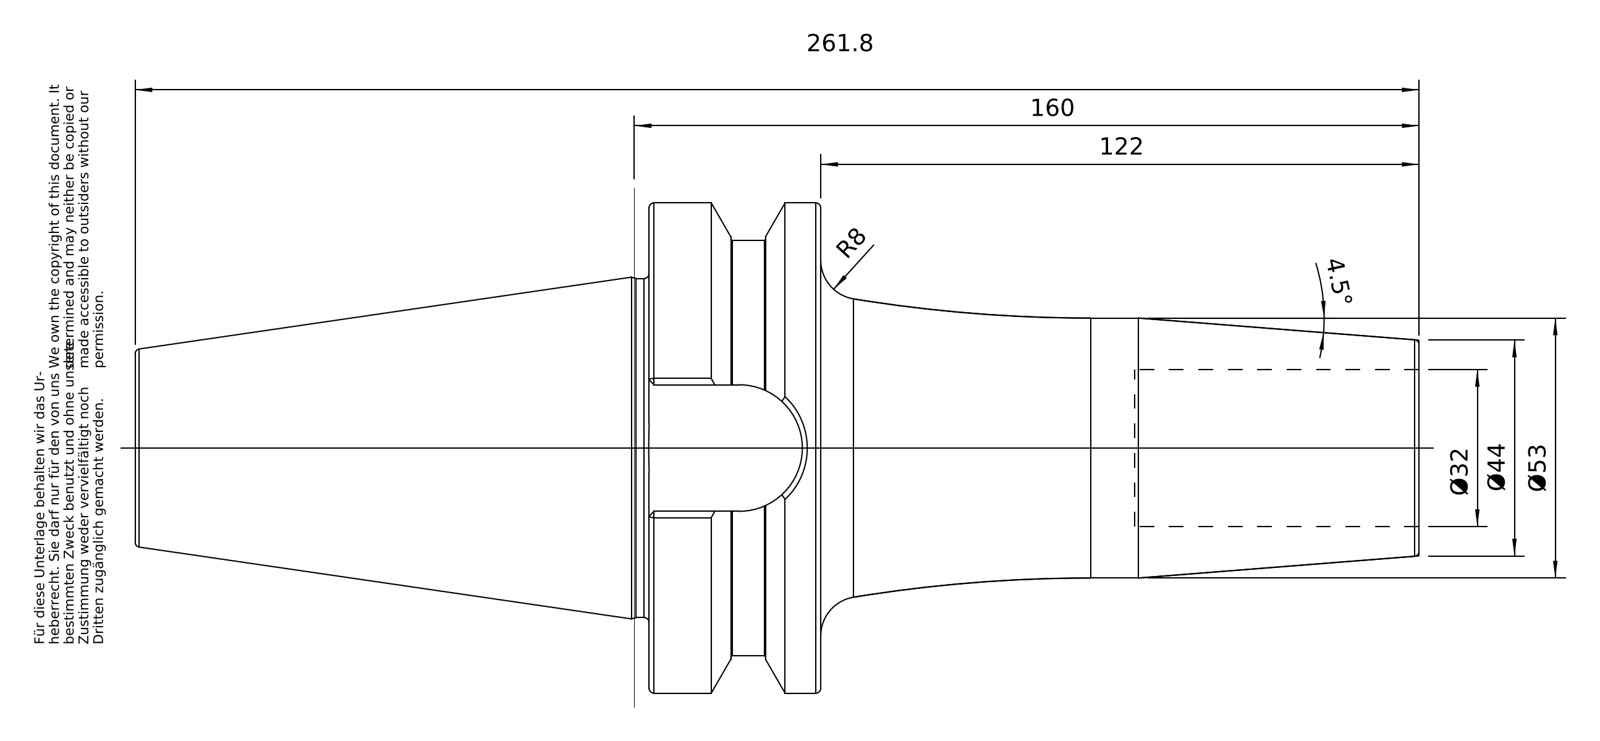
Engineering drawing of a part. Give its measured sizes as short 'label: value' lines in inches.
name: 50-642-32
written by: PRO/ENGINEER BY PARAMETRIC TECHNOLOGY CORPORATION, 2010430 (CONFIG_CONTROL_DESIGN)
unit: in
bodies: 1 solid, 98 faces (26 planar, 22 cylindrical, 50 other)
size: 10.307 × 3.936 × 3.936
volume: 42.02 in³; area: 117.4 in²
holes: 1× ⌀0.817, 1× ⌀0.985, 1× ⌀1.012, 1× ⌀1.26
bosses: 1× ⌀3.936, 1× ⌀3.337, 1× ⌀2.722, 1× ⌀2.087, 1× ⌀0.945
rounds: 1× R0.508
face distances: 1.378, 3.898, 2.52, 2.772, 6.181, 4.803, 2.283, 4.126, 5.504, 8.024
